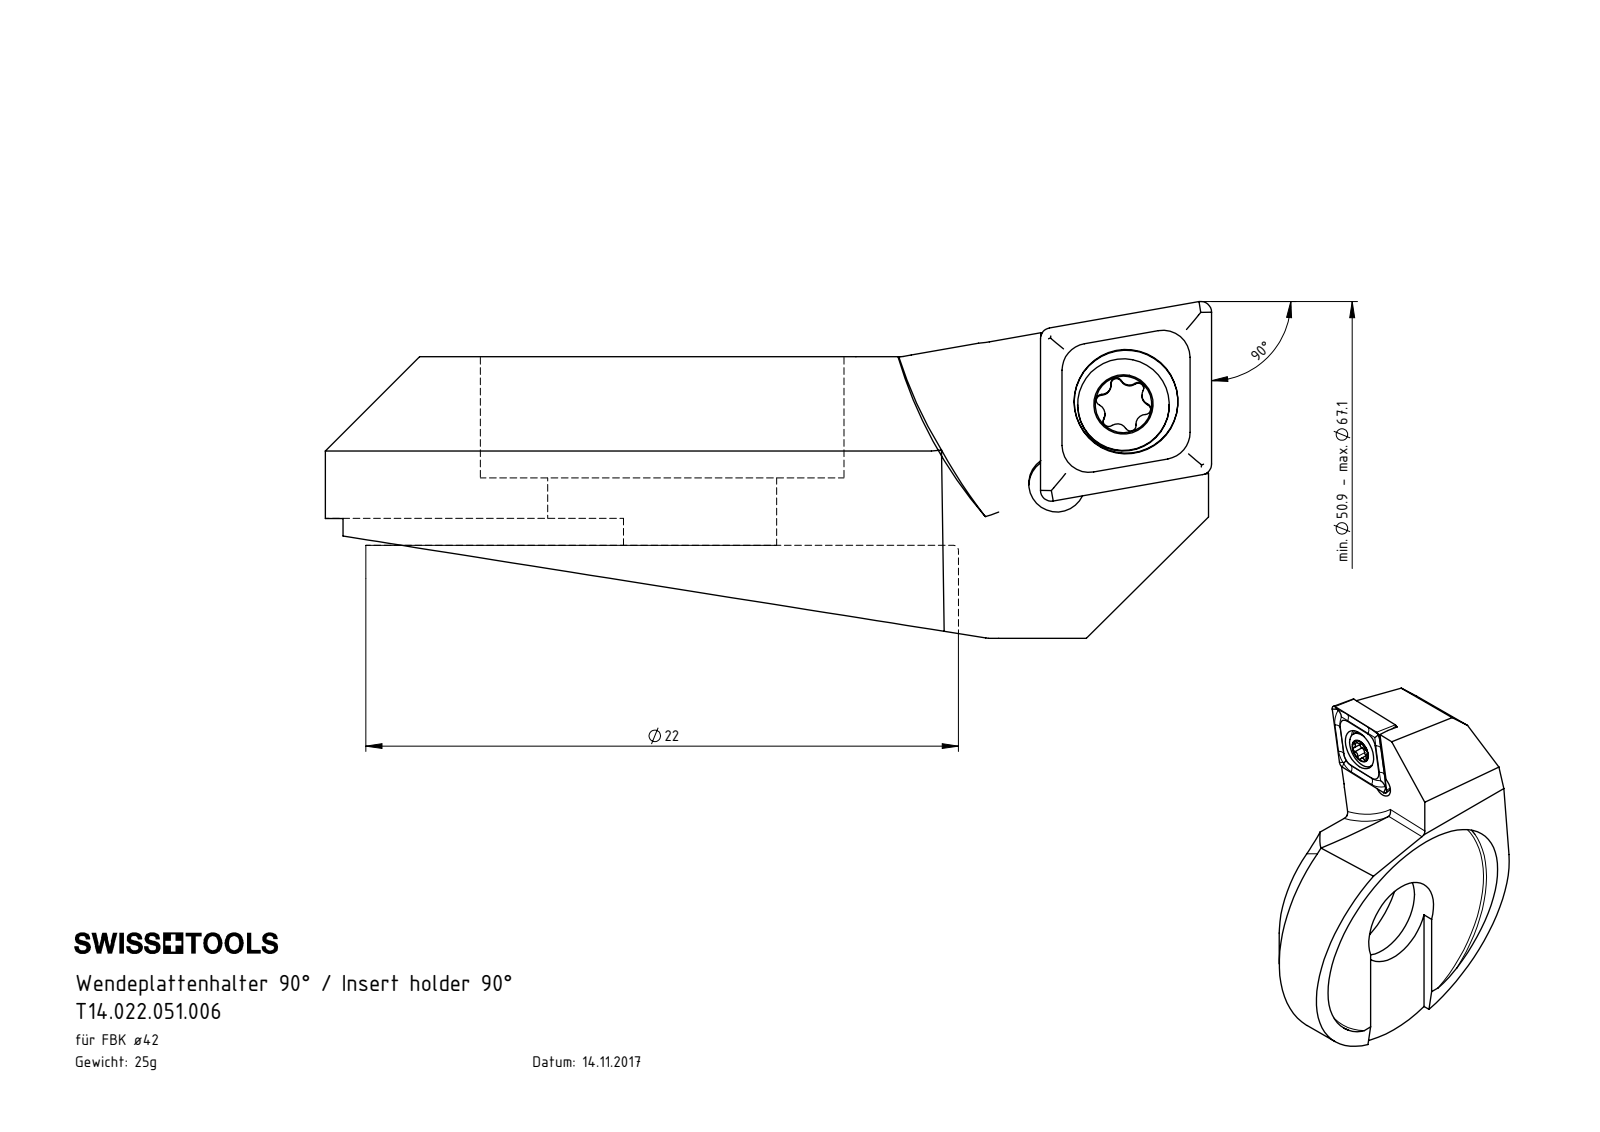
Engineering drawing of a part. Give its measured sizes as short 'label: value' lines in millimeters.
name: F42.WCA.001.009; F42-WCA.001.009_C_fertigbearbeitet; WCA-ER2.001.006_A; CCMT060204
written by: SolidWorks 2017 (AUTOMOTIVE_DESIGN)
unit: mm
bodies: 3 solids, 103 faces (39 planar, 26 cylindrical, 38 other)
size: 32.9 × 25 × 12.5
volume: 3 141 mm³; area: 2 312 mm²
holes: 1× ⌀2.05, 1× ⌀2.1, 1× ⌀2.8, 1× ⌀3.85, 1× ⌀8.5, 1× ⌀13.5
bosses: 1× ⌀3.4, 1× ⌀2.5
rounds: 6× R0.21, 5× R0.36, 2× R0.5, 1× R0.36, 1× R5, 1× R11, 1× R12.5, 1× R16
face distances: 7, 4.5, 2.5, 6, 1.5, 1, 2.28, 10.45, 5.95, 4.45
hole spacings: 3.84, 3.99
